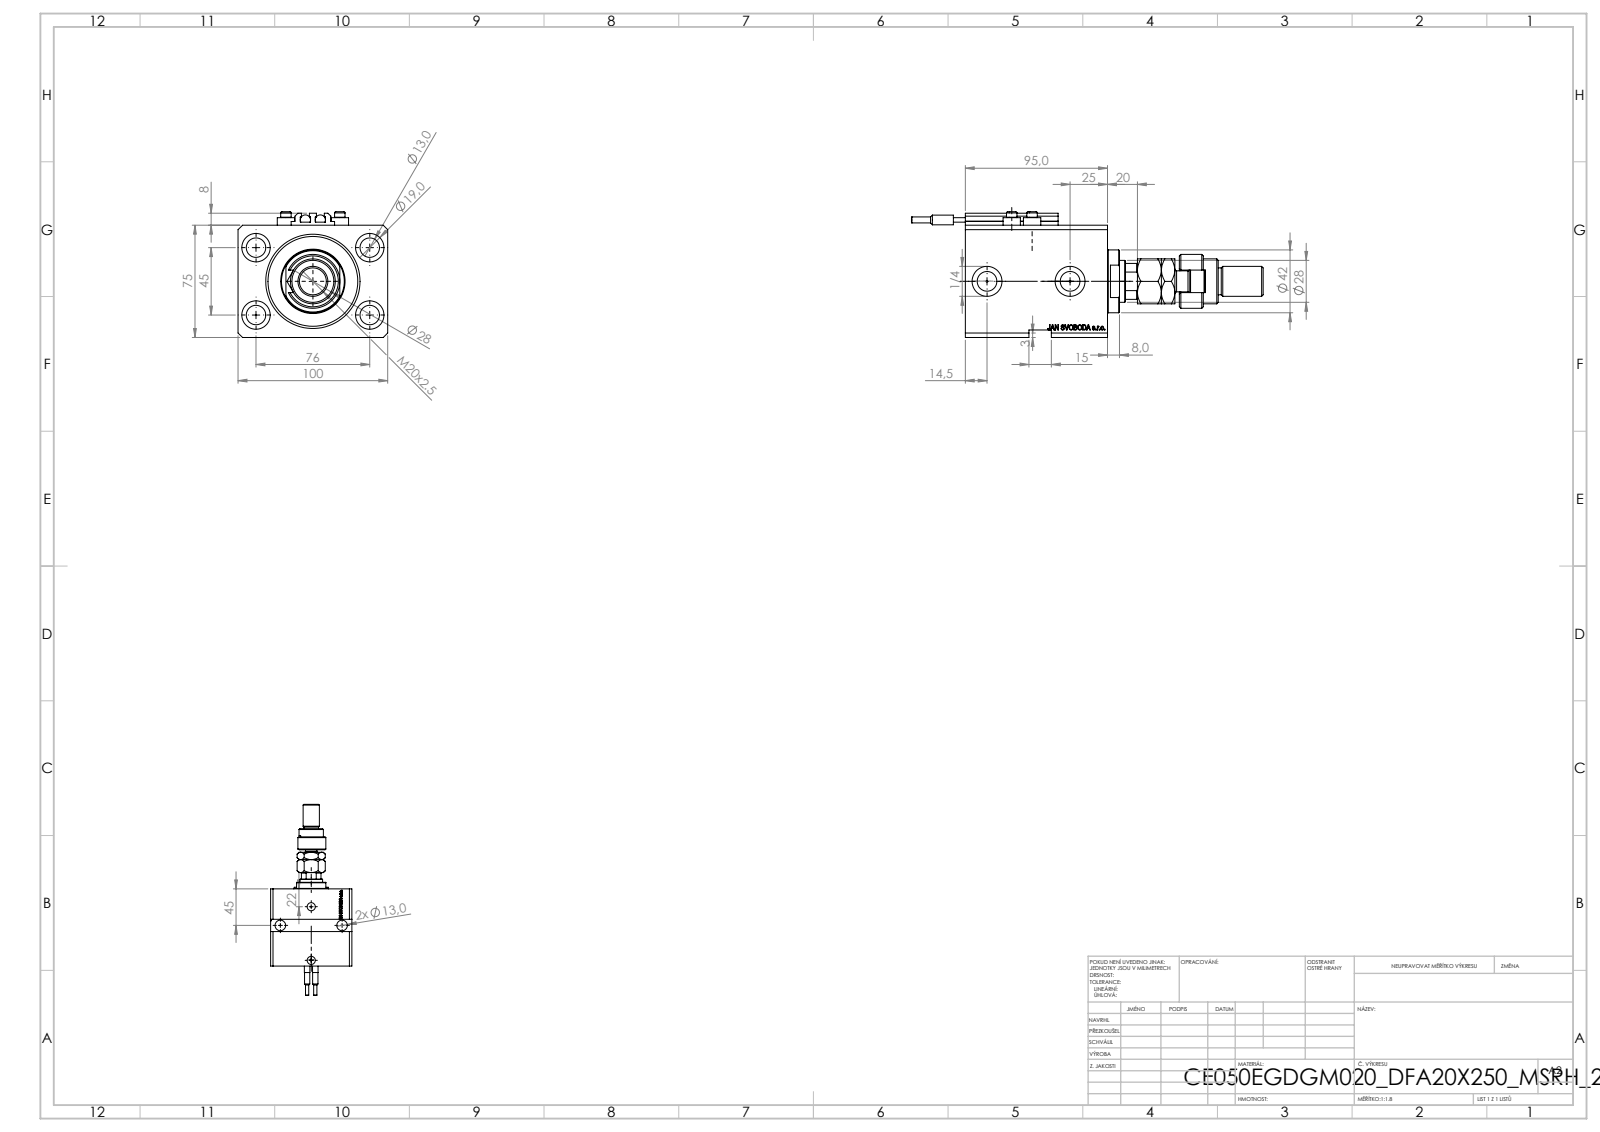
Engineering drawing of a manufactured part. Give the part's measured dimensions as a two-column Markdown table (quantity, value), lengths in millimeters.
| quantity | value |
| --- | --- |
| part name | V250CE_C_VCP; MFA; FEMALE_PART_FOR_DFA; V250CE_VC_E (+3 more) |
| STEP written by | SolidWorks 2019 (CONFIG_CONTROL_DESIGN) |
| units | millimeters |
| bodies | 12 solids, 1241 faces (599 planar, 163 cylindrical, 479 other) |
| overall size | 235 × 100 × 84 |
| volume | 659 841 mm³ |
| surface area | 139 062 mm² |
| round holes (diameter × count) | 13 × 6, 1.25 × 4, 4 × 4, 19 × 4, 10 × 2, 13.16 × 2, 20 × 2, 18.5 × 1, 28 × 1, 50 × 1, 63 × 1 |
| round bosses / shafts (diameter × count) | 11.6 × 4, 7 × 4, 6.8 × 2, 6.5 × 2, 4 × 2, 42 × 1, 36 × 1, 30 × 1 |
| partial cylindrical surfaces (radius × count) | 0.2 × 10, 7.5 × 1, 12 × 1, 13.5 × 1 |
| main face-to-face distances | 75, 20, 100, 95, 11.9, 83.1, 63.1, 40, 5, 3 |
| hole center spacings | 44.16, 76, 13.6, 20.72, 27.59, 29.58, 30, 33.62 |
